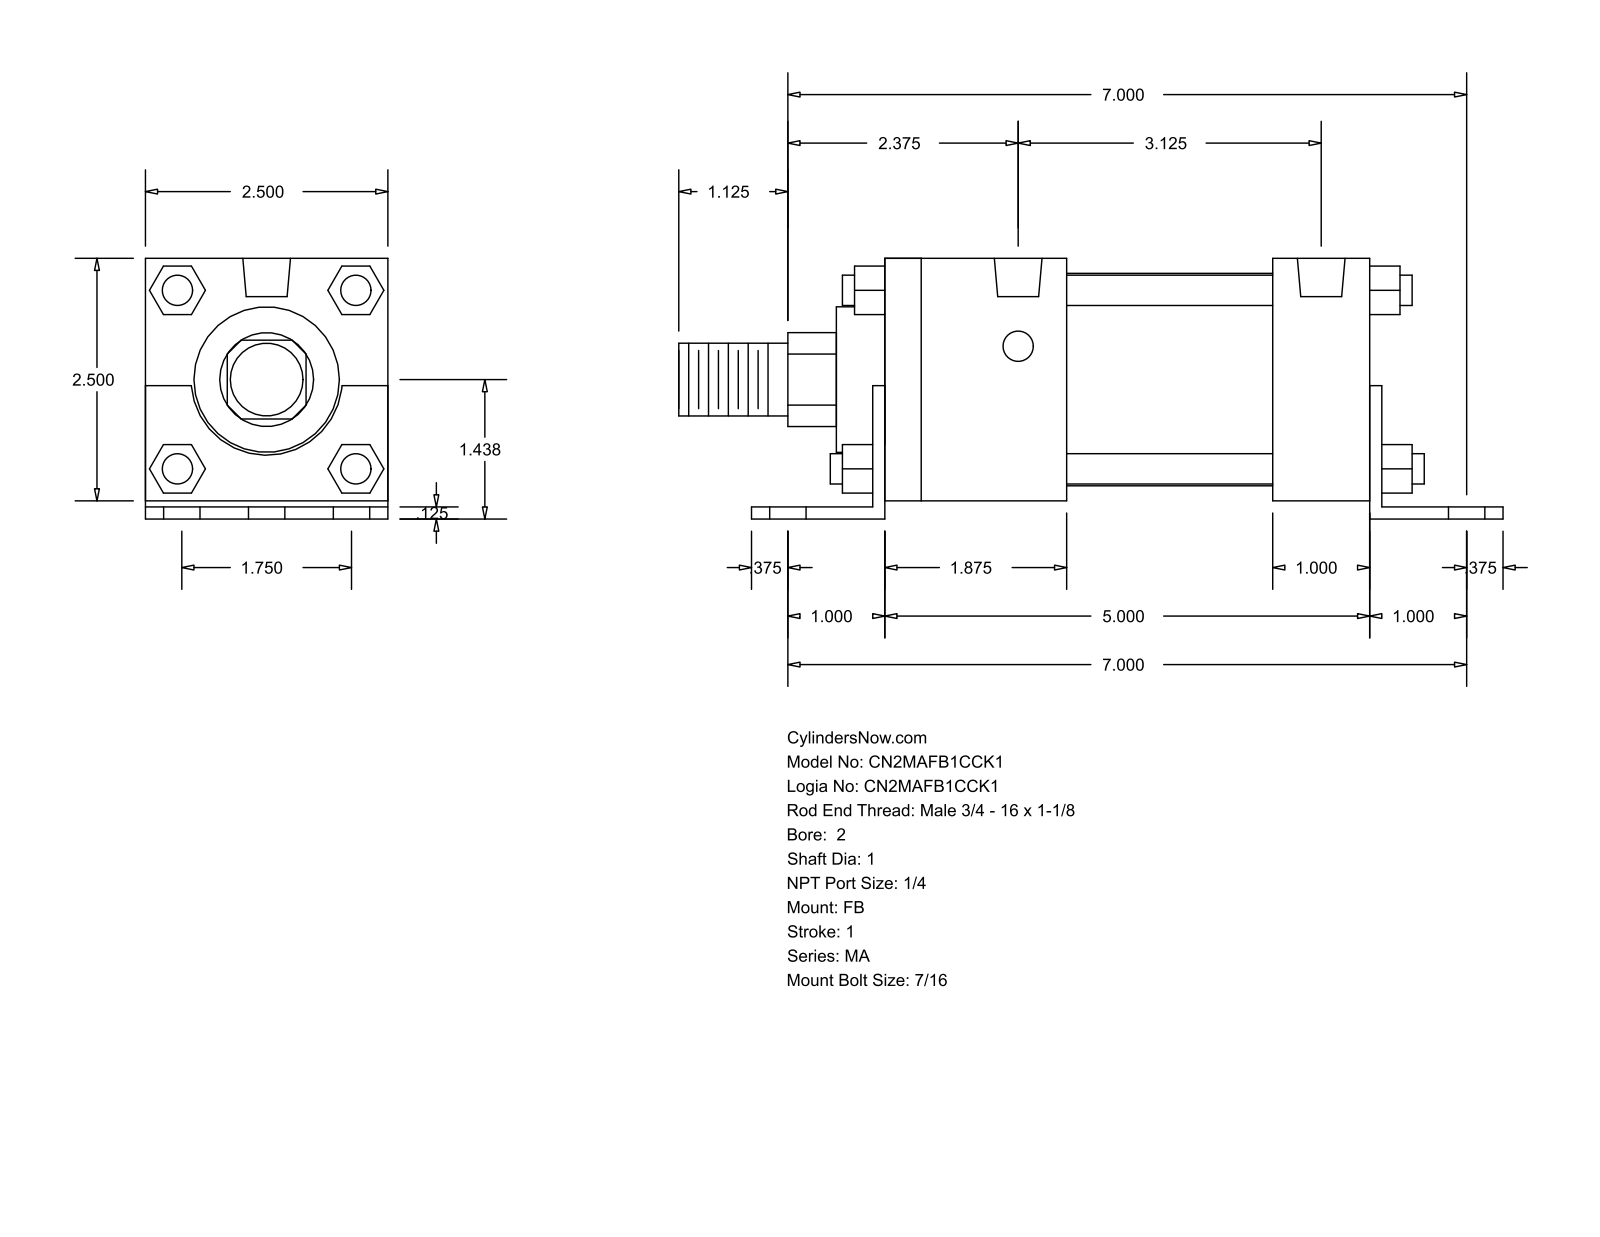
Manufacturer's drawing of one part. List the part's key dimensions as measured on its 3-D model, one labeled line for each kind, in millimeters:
Part name (STEP PRODUCT): MA_FB__0200_1
STEP written by: GSSL Pune (CONFIG_CONTROL_DESIGN)
Units: millimetres
Bodies: 0 solids, 140 faces (105 planar, 35 cylindrical, 0 other)
Overall size (bounding box): 215.9 × 68.26 × 63.5
Round holes (diameter × count): ⌀11.11 ×6, ⌀7.94 ×4, ⌀12.49 ×2
Round bosses / shafts (diameter × count): ⌀7.94 ×4, ⌀55.63 ×1, ⌀38.1 ×1, ⌀25.4 ×1, ⌀19.05 ×1
Partial cylindrical surfaces — rounded edges, fillets, slot ends (radius × count): R12.29 ×1, R19.81 ×1
Main face-to-face distances: 63.5, 3.17, 4.76, 68.26, 1.59, 65.09, 130.17, 12.7, 53.97, 101.6
Hole centre spacings: 22.23, 179.18, 177.8, 44.11, 44.46, 64.3, 79.37, 119.55
